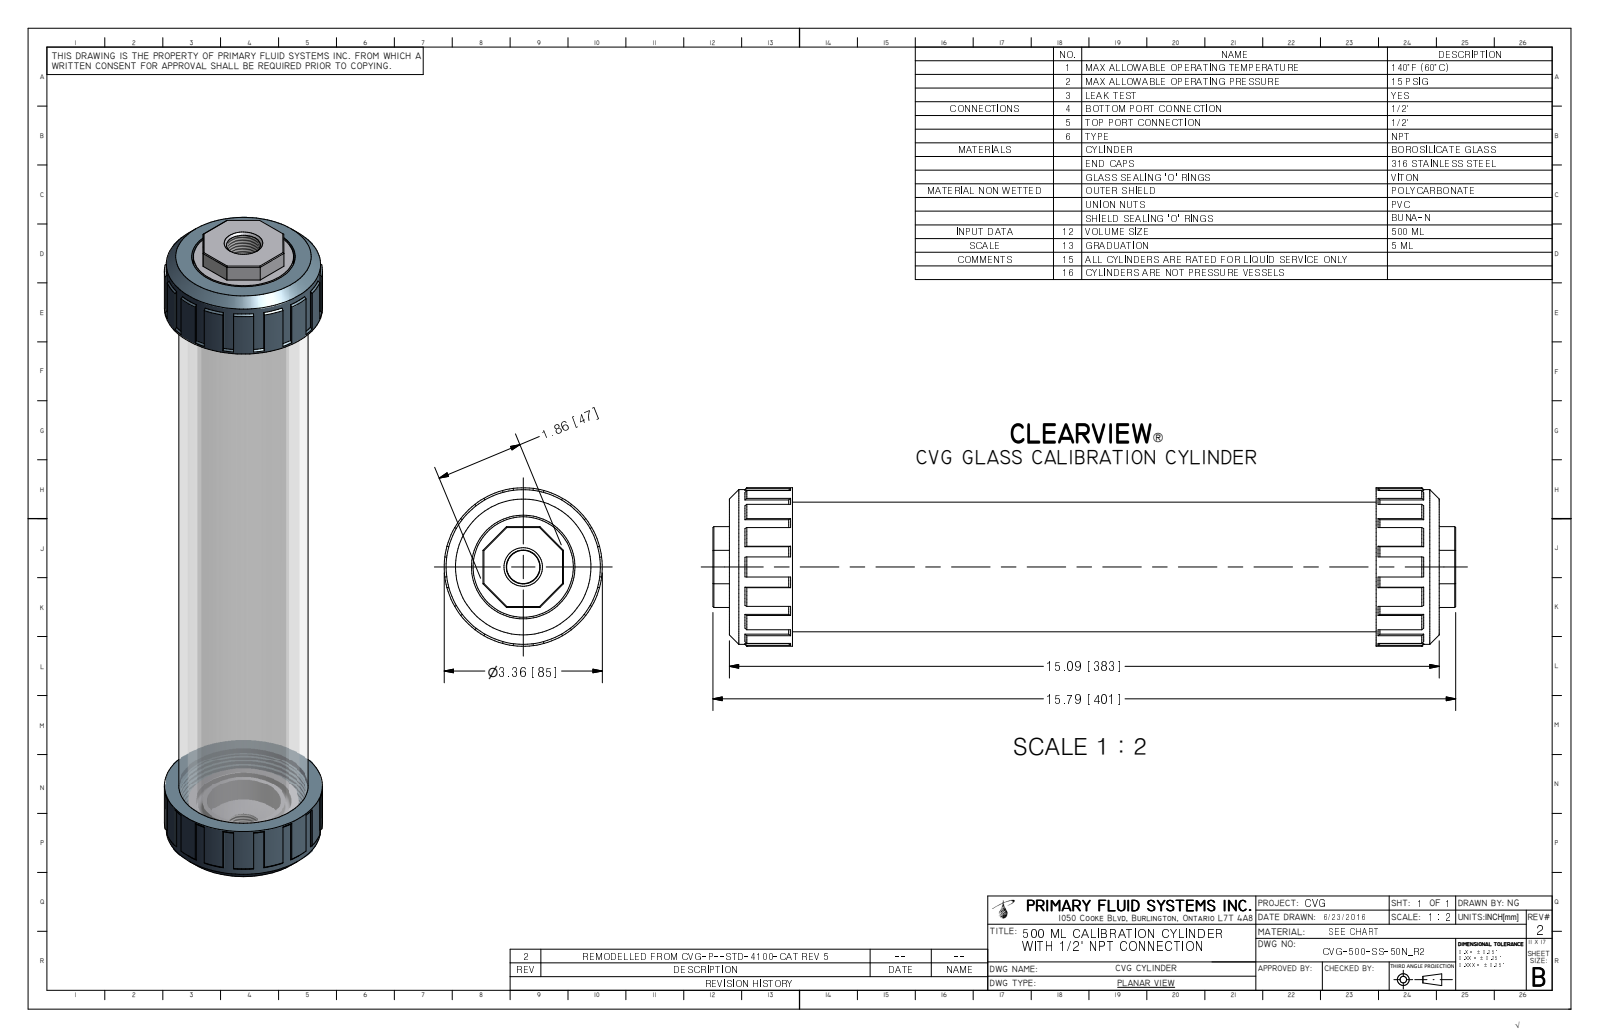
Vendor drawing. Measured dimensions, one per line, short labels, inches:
name: CVG-500-SS-50N_R2; CVG-3-500-METAL-NPT-50_R4; CVG-1-500-A_R0; CVG-6-500 (+1 more)
written by: Autodesk Inventor 2009 (AUTOMOTIVE_DESIGN)
unit: in
bodies: 6 solids, 309 faces (88 planar, 35 cylindrical, 186 other)
size: 15.79 × 3.36 × 3.36
volume: 40.28 in³; area: 522.4 in²
holes: 1× ⌀0.719, 1× ⌀1.555, 1× ⌀1.811, 1× ⌀2.05, 1× ⌀2.4
bosses: 1× ⌀2.75, 1× ⌀2.661, 1× ⌀2.66, 1× ⌀2.49, 1× ⌀2.36, 1× ⌀2.226, 1× ⌀2.13, 1× ⌀1.969
face distances: 1.3, 14.49, 0.648, 15.142, 0.652, 13.842, 0.35, 15.44, 0.298, 0.95
